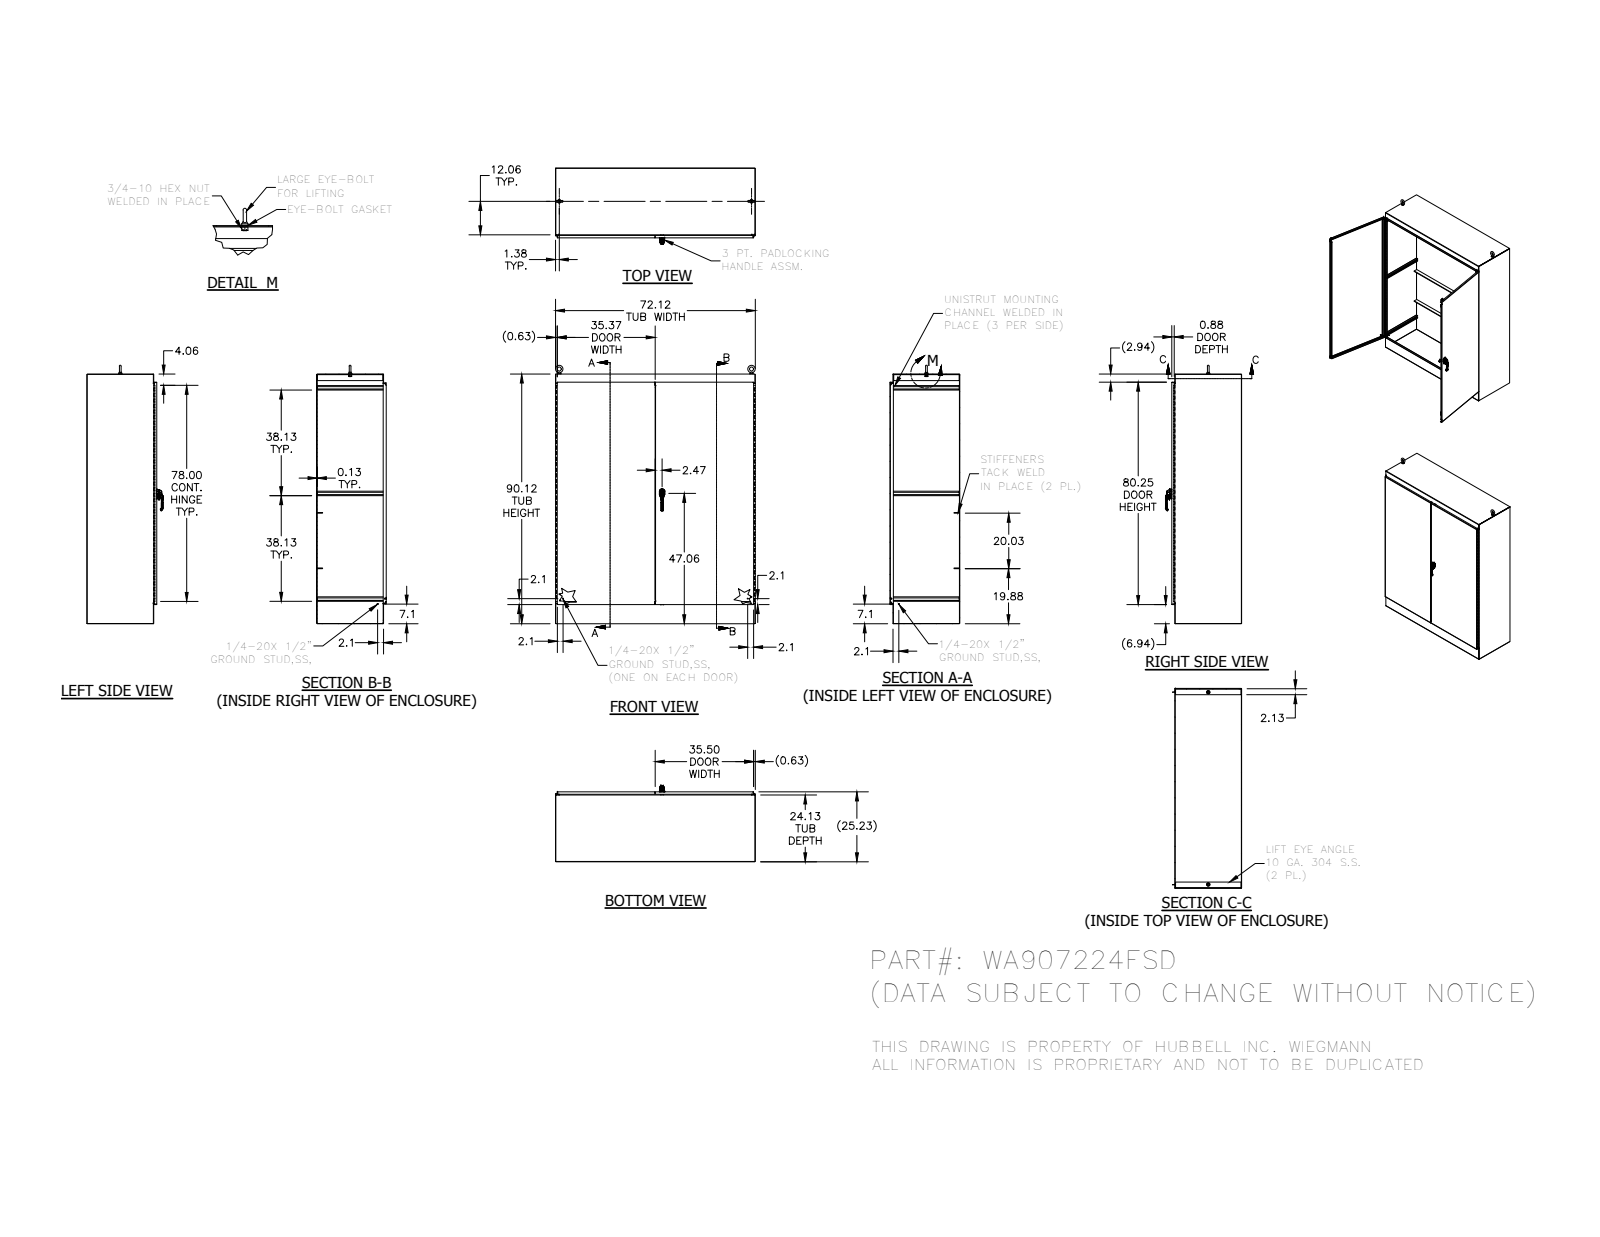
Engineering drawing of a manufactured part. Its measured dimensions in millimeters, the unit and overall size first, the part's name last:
Units: millimetres
Overall size (bounding box): 2368.49 × 1832.09 × 698.45
Round holes (diameter × count): ⌀9.52 ×16, ⌀7.02 ×8, ⌀5.08 ×4, ⌀5.4 ×3, ⌀6 ×3, ⌀7.11 ×3, ⌀3.61 ×2, ⌀4.57 ×2, ⌀6.13 ×2, ⌀6.35 ×2, ⌀6.41 ×2, ⌀10.16 ×2
Round bosses / shafts (diameter × count): ⌀8.56 ×3, ⌀6.35 ×3, ⌀31.75 ×2, ⌀28.45 ×2, ⌀25.4 ×2, ⌀19.05 ×2, ⌀14.29 ×2, ⌀13.37 ×2
Partial cylindrical surfaces — rounded edges, fillets, slot ends (radius × count): R0.5 ×166, R0.3 ×89, R0.79 ×24, R3.97 ×21, R3.17 ×20, R0.47 ×19, R0.25 ×16, R2 ×15
Main face-to-face distances: 3.18, 3.17, 637.66, 634.48, 640.83, 637.65, 1828.8, 2286, 1825.62, 1831.98
Hole centre spacings: 220.13, 660.4, 440.27, 1798.26, 1804.99, 1818.36, 880.53, 1838.24
Volume: 48 820 000 mm³ · Surface area: 30 760 000 mm²
Bodies: 66 solids, 3742 faces (1767 planar, 1237 cylindrical, 738 other)
Part name (STEP PRODUCT): FUN00103; HFW3025; 316298; 349132 (+8 more)
STEP written by: Autodesk Inventor 2014 (AUTOMOTIVE_DESIGN)
